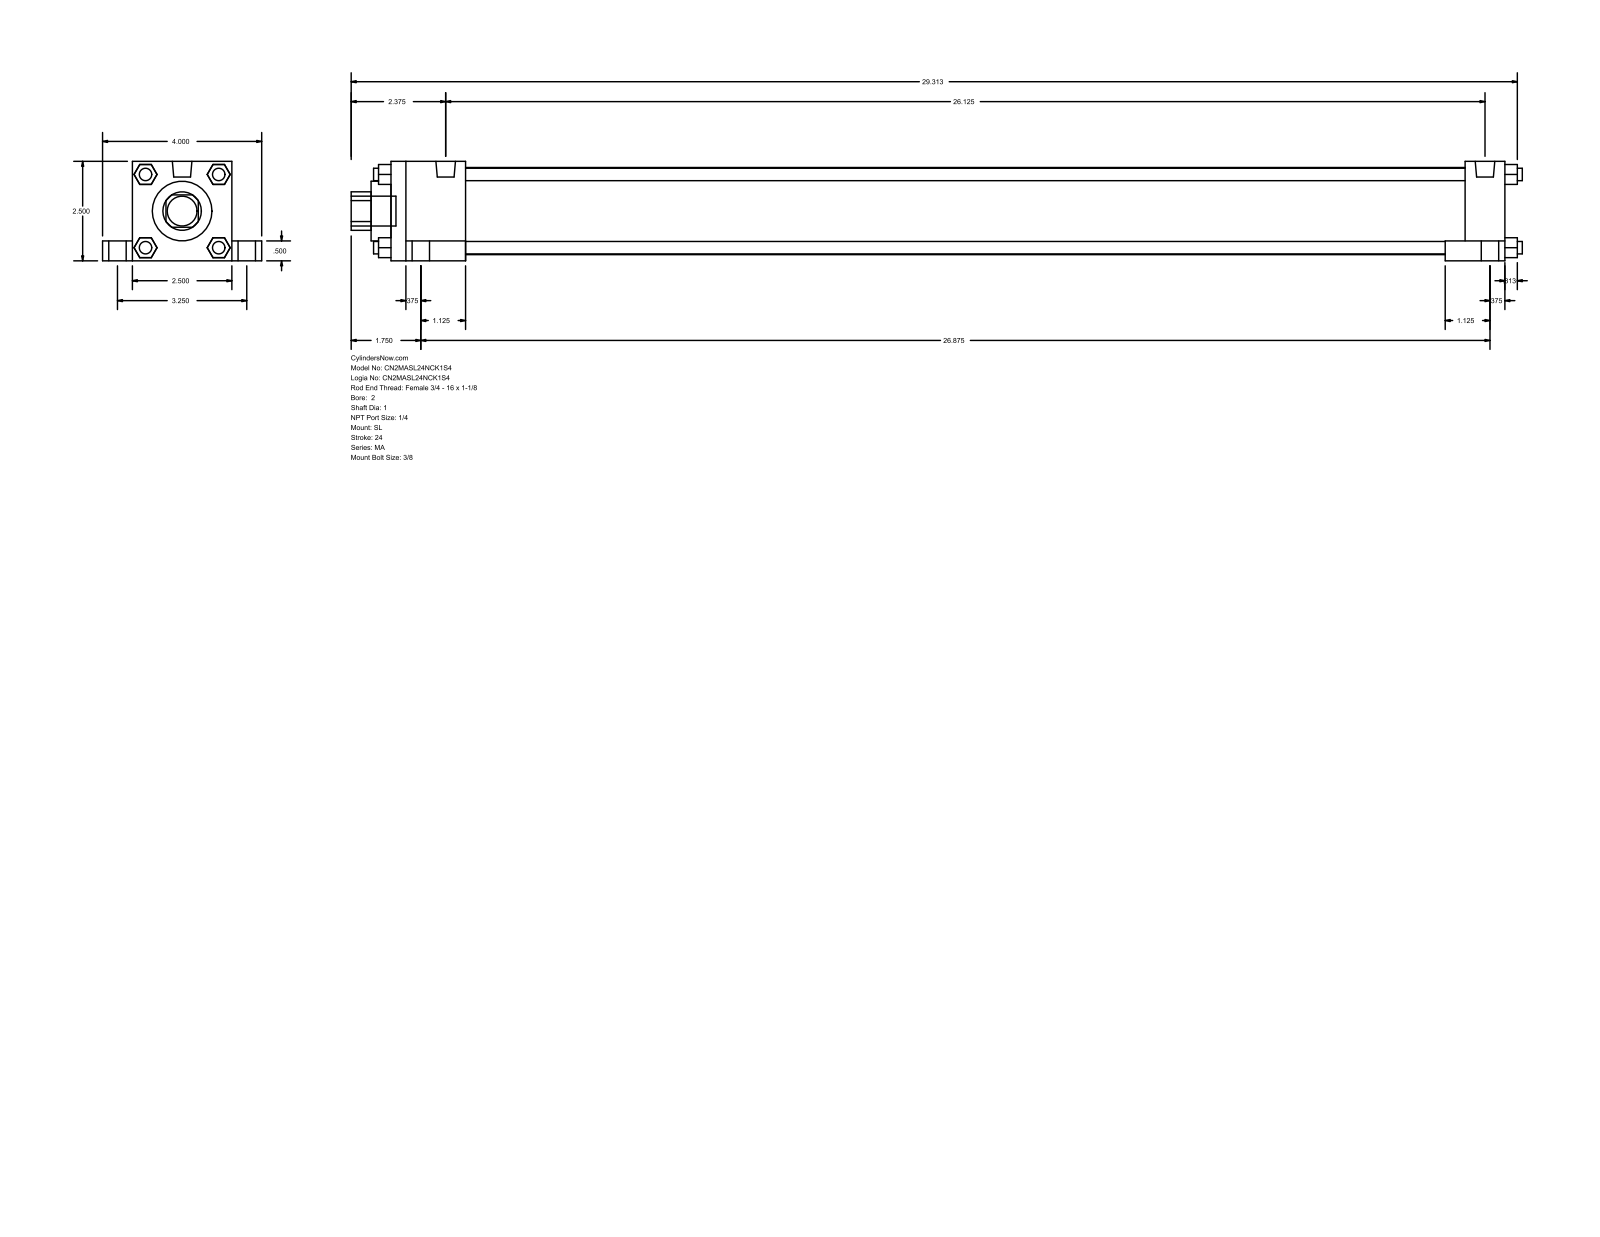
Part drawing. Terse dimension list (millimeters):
name: MA_SL__0200_1
written by: GSSL Pune (CONFIG_CONTROL_DESIGN)
unit: mm
bodies: 0 solids, 148 faces (112 planar, 36 cylindrical, 0 other)
size: 747.71 × 101.6 × 63.5
holes: 1× ⌀25.4, 1× ⌀38.1, 1× ⌀55.63
bosses: 8× ⌀7.94, 4× ⌀17.46, 4× ⌀11.11, 2× ⌀12.49, 1× ⌀19.05
rounds: 1× R12.29
face distances: 63.5, 12.7, 711.2, 19.05, 82.55, 25.4, 50.8, 47.63, 663.57, 685.8
